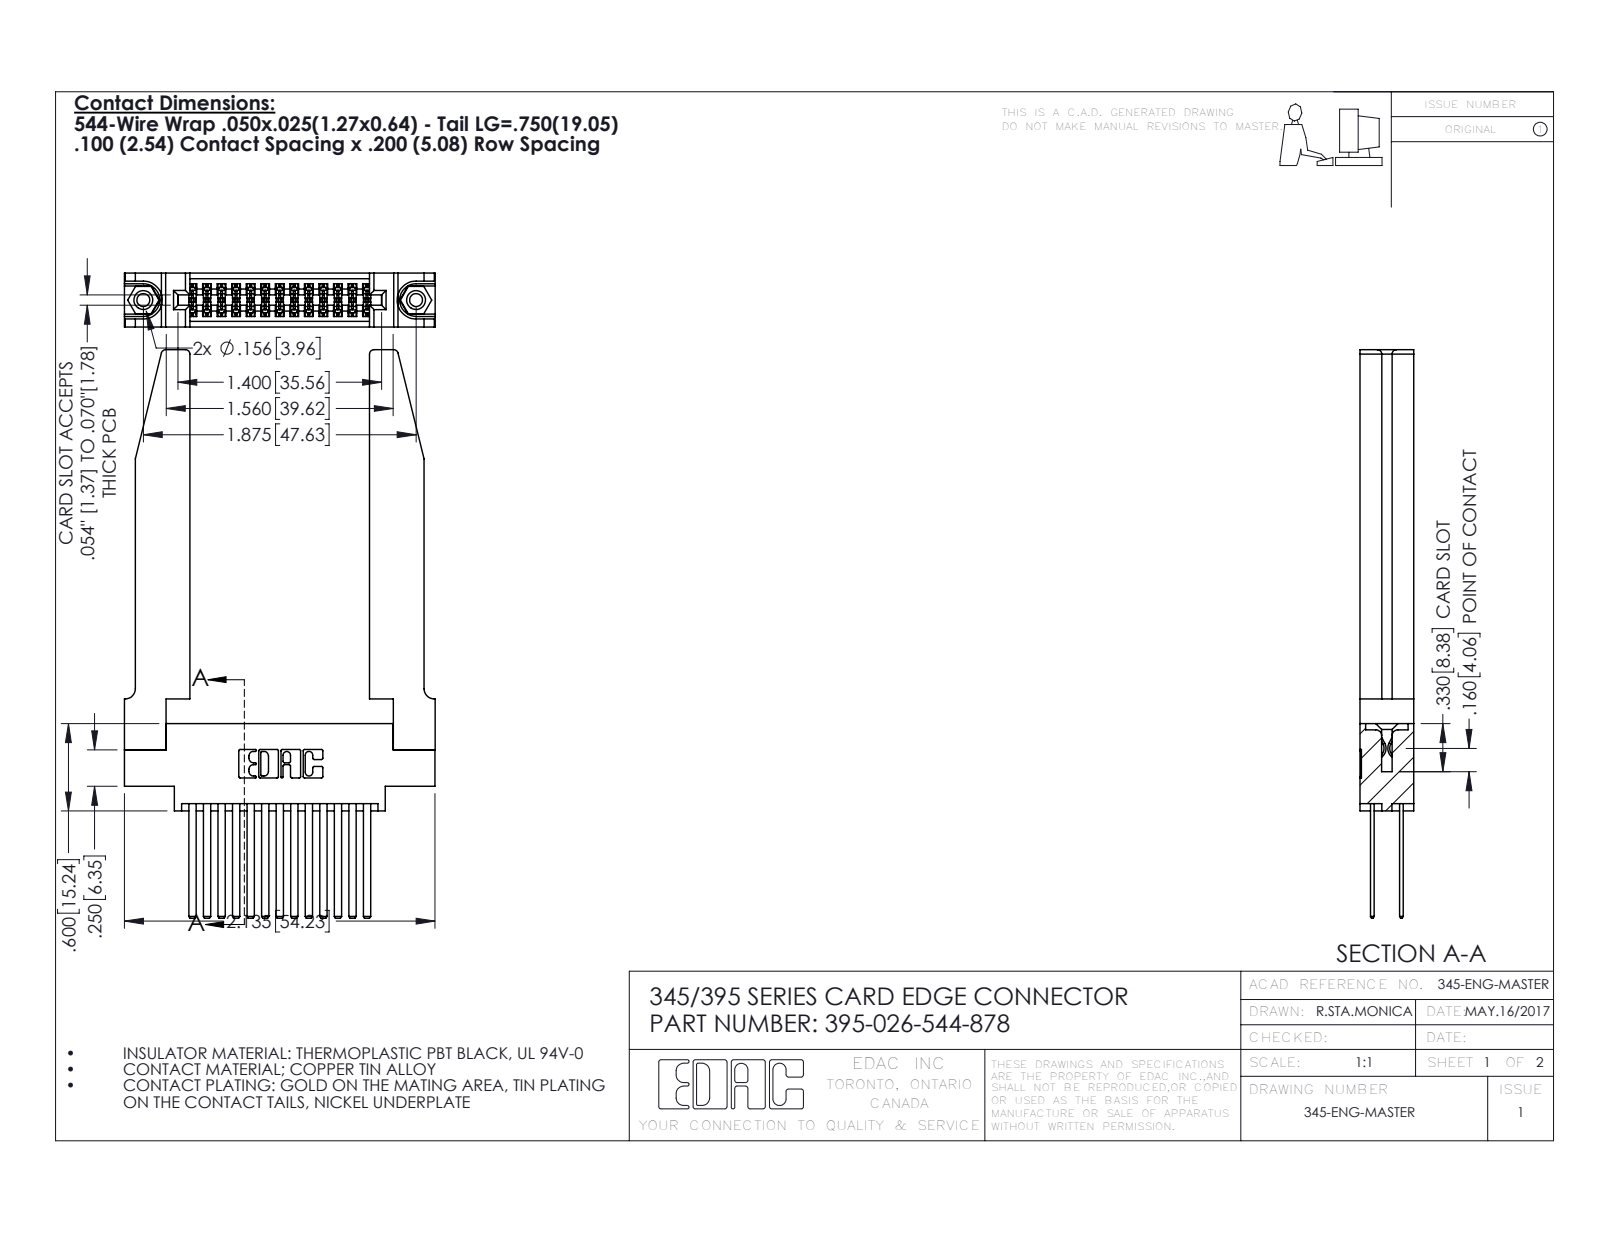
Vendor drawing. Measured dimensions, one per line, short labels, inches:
name: 345-250-001_345-250-001-102; 345-220-078_345-220-078; 345 Part_0.170 Offset - 0.156 Dia-TH; 395-026-544-878 (+1 more)
written by: SolidWorks 2016 (CONFIG_CONTROL_DESIGN)
unit: in
bodies: 31 solids, 1508 faces (980 planar, 476 cylindrical, 52 other)
size: 3.907 × 2.136 × 0.37
volume: 0.795 in³; area: 23.64 in²
holes: 2× ⌀0.089, 2× ⌀0.125, 2× ⌀0.156, 1× ⌀0.064
bosses: 2× ⌀0.155
rounds: 39× R0.006, 22× R0.01, 8× R0.03, 6× R0.007, 6× R0.031, 3× R0.026, 2× R0.014, 2× R0.019
face distances: 0.37, 0.072, 0.298, 0.098, 0.272, 0.025, 0.2, 0.225, 0.175, 0.148
hole spacings: 0.27, 1.643, 1.875
